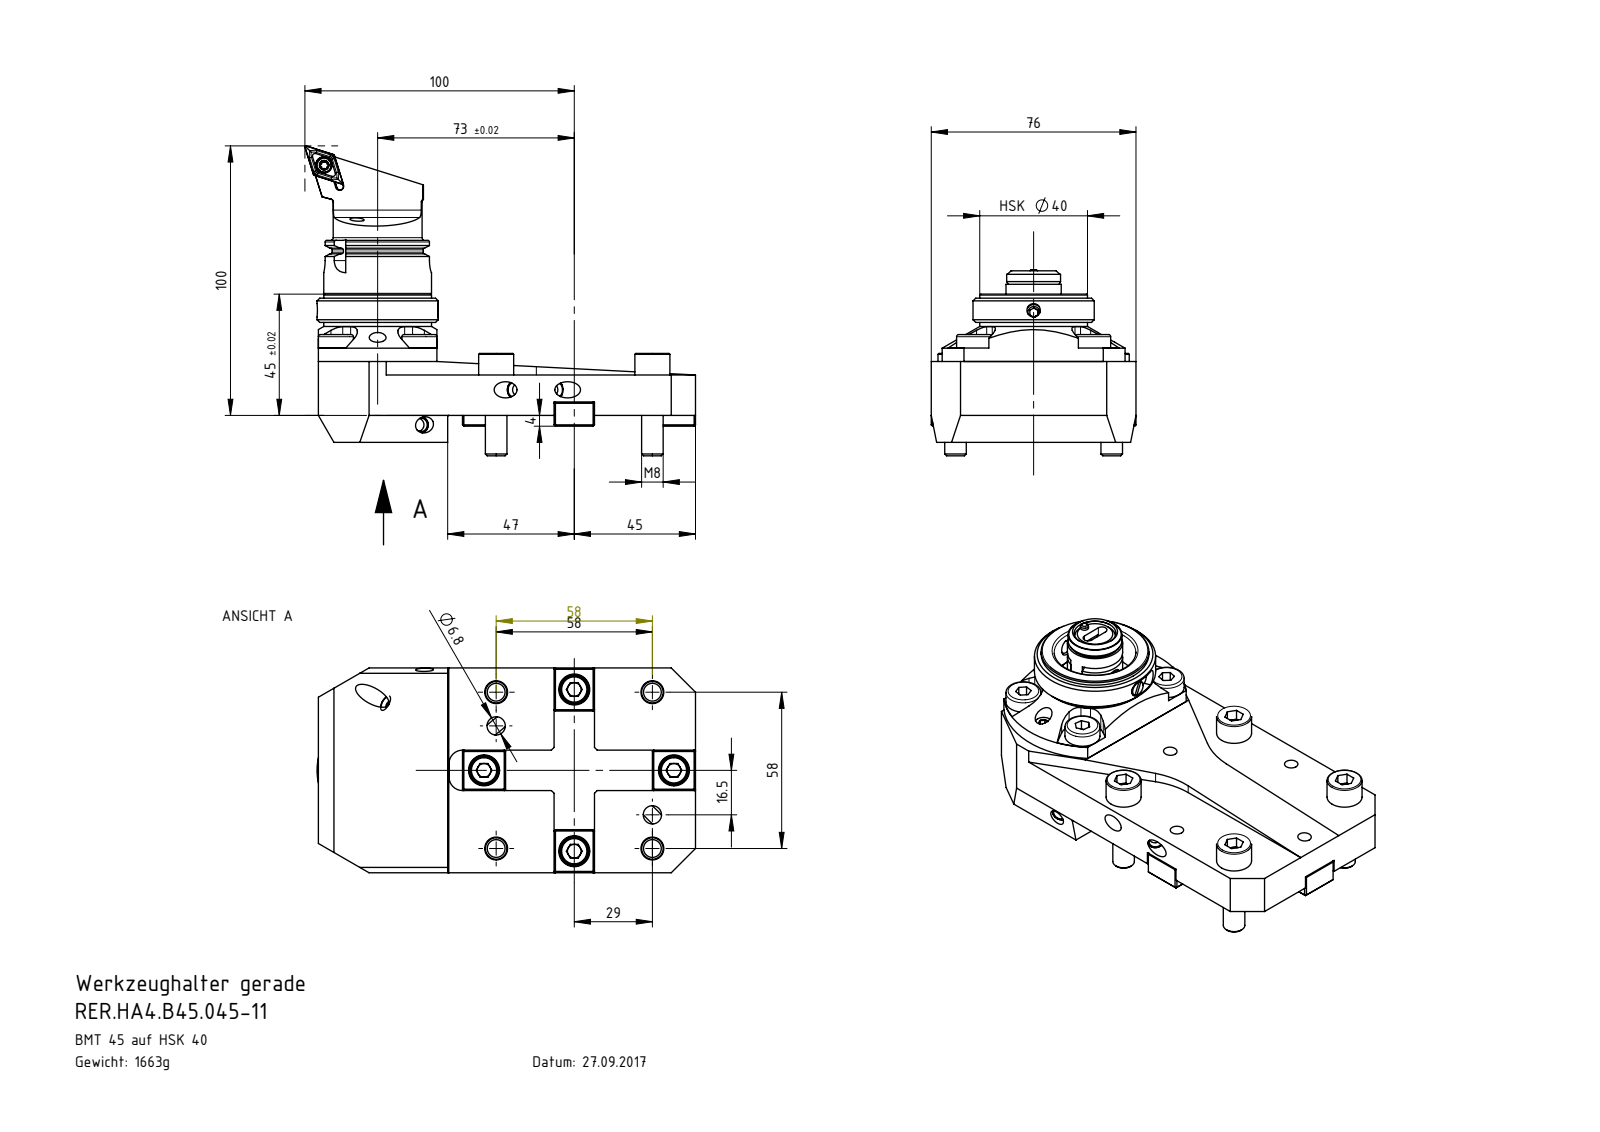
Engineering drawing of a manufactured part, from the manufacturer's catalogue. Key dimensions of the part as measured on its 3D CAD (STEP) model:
Part name (STEP PRODUCT): HA4-KDB.RHA.055_A_Fertigbearbeitung; Dichtung; U40-HA4.001.025; DIN 7984 - M8 x 25 (+8 more)
STEP written by: SolidWorks 2017 (AUTOMOTIVE_DESIGN)
Units: millimetres
Bodies: 51 solids, 1530 faces (552 planar, 422 cylindrical, 556 other)
Overall size (bounding box): 145 × 112 × 76
Volume: 284 094 mm³ · Surface area: 102 682 mm²
Round holes (diameter × count): ⌀5 ×16, ⌀6.8 ×6, ⌀6 ×5, ⌀11 ×5, ⌀6.5 ×4, ⌀7 ×4, ⌀8.4 ×4, ⌀8.5 ×4, ⌀9 ×4, ⌀4.2 ×3, ⌀1.6 ×2, ⌀3 ×2
Round bosses / shafts (diameter × count): ⌀6 ×10, ⌀8 ×8, ⌀10 ×5, ⌀16 ×4, ⌀13 ×4, ⌀45 ×1, ⌀40 ×1, ⌀39.5 ×1
Partial cylindrical surfaces — rounded edges, fillets, slot ends (radius × count): R5 ×11, R1 ×8, R0.34 ×6, R0.59 ×6, R0.9 ×6, R1.95 ×4, R2 ×4, R4.5 ×4
Main face-to-face distances: 15, 10, 5, 25, 20, 30, 76, 13, 12, 1.6
Hole centre spacings: 22.32, 26.99, 29.02, 35.59, 58, 65.74, 3.67, 6.61
